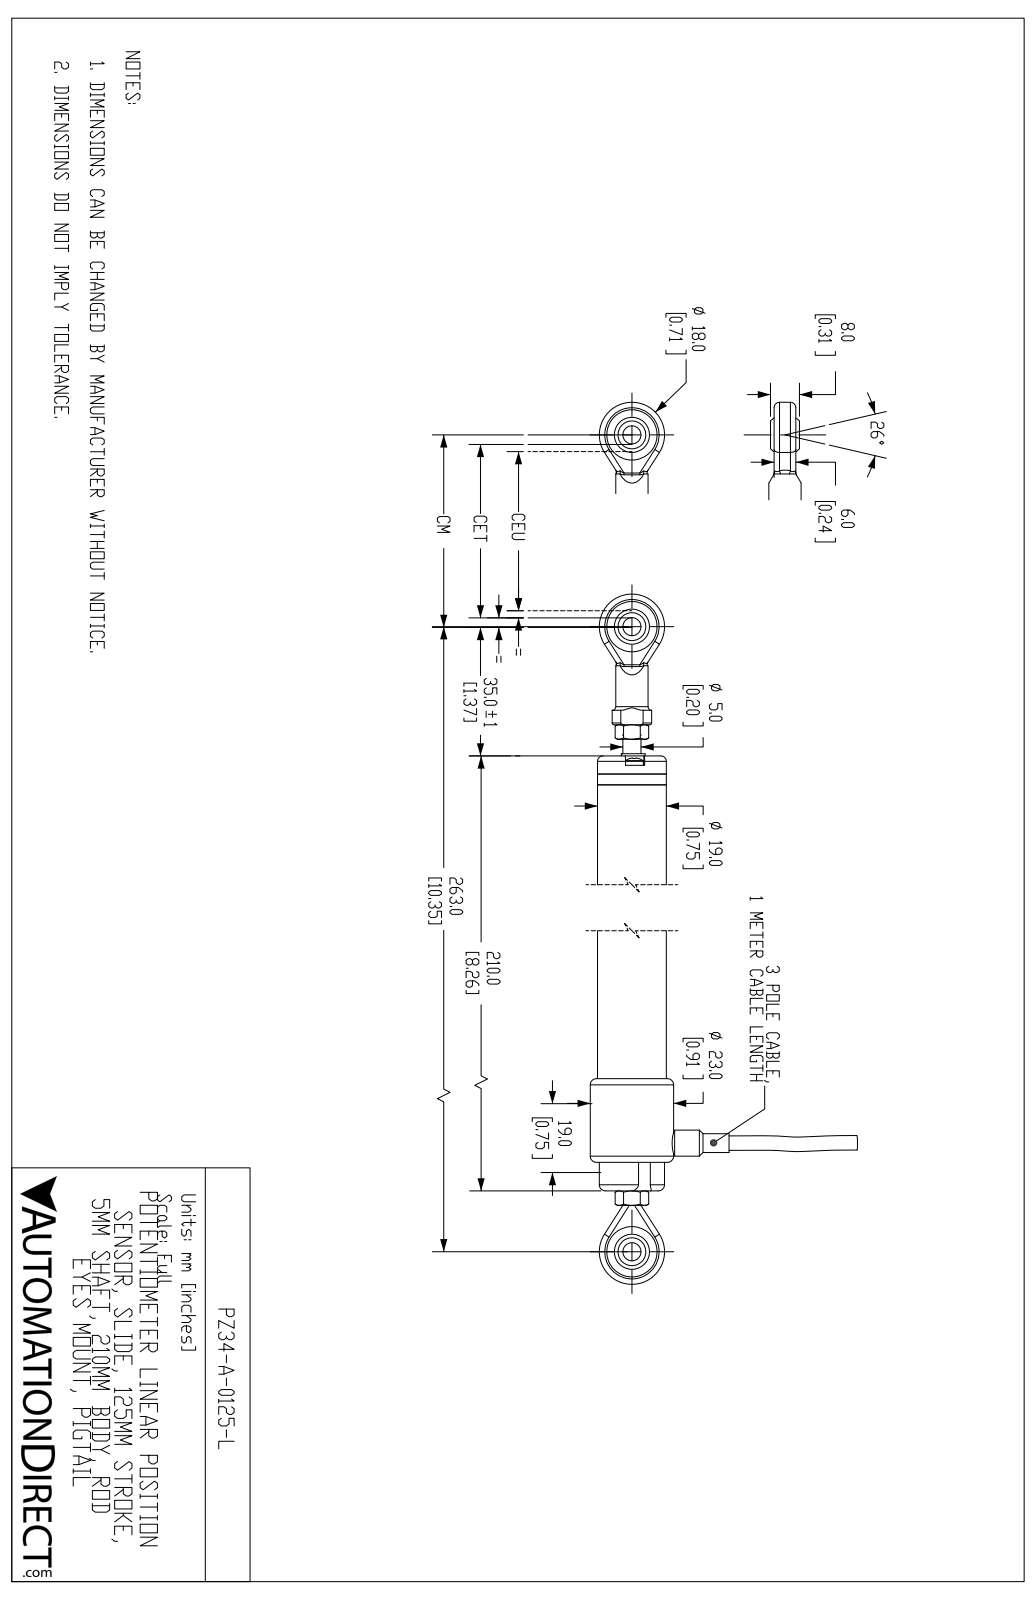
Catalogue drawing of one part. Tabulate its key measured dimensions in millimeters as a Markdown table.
| quantity | value |
| --- | --- |
| part name | PZ34-A-0125-L |
| STEP written by | SolidWorks 2019 (AUTOMOTIVE_DESIGN) |
| units | millimeters |
| bodies | 18 solids, 916 faces (334 planar, 198 cylindrical, 384 other) |
| overall size | 280.5 × 73.8 × 23 |
| volume | 72 630 mm³ |
| surface area | 28 280 mm² |
| round holes (diameter × count) | 2 × 4, 2.9 × 4, 5 × 2, 5.3 × 2, 13.9 × 2, 3.5 × 1, 4.2 × 1, 6.1 × 1, 9 × 1, 19.1 × 1 |
| round bosses / shafts (diameter × count) | 5 × 5, 2.5 × 4, 23 × 1, 19 × 1, 18 × 1, 8.9 × 1, 7.2 × 1, 6 × 1 |
| partial cylindrical surfaces (radius × count) | 1.5 × 8, 0.3 × 4, 0.5 × 2, 1 × 2, 2.6 × 2, 9 × 2, 0.4 × 1, 1.6 × 1 |
| main face-to-face distances | 187, 184, 3, 8, 5.7, 5.4, 5.5, 1.3, 1, 6.7 |
| hole center spacings | 6.8, 2.1, 13.5, 13.7, 262.5 |
